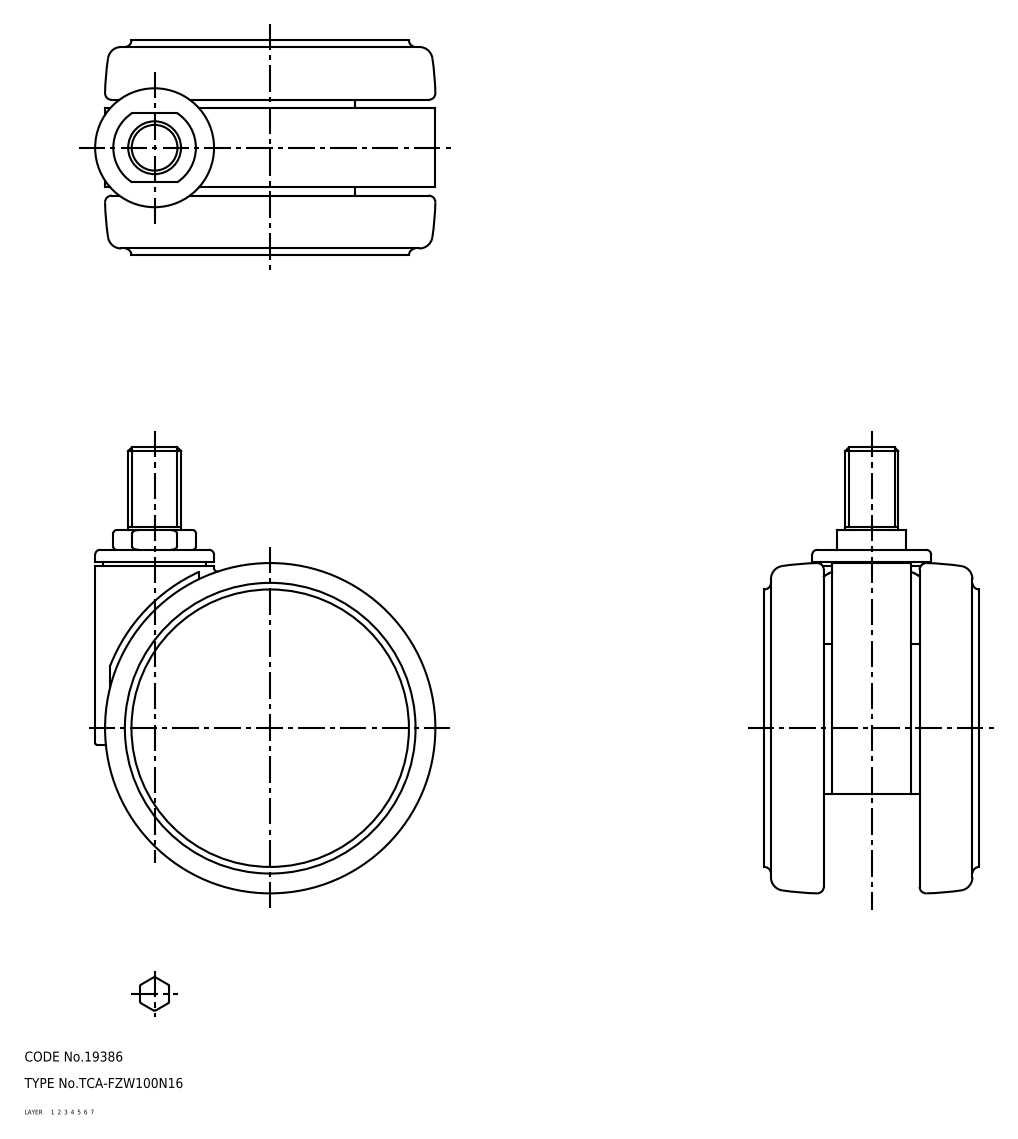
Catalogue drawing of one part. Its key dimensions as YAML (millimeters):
part_name: "caster; TCA-FZW100N16"
step_written_by: "SolidWorks 2015 (AUTOMOTIVE_DESIGN)"
units: millimeters
bodies: {solids: 1, faces: 2344, planar: 792, cylindrical: 1084, other: 468}
overall_size: [135, 103, 65.2]
volume: 299278
surface_area: 123312
round_holes:
  - {diameter: 9.1, count: 1}
  - {diameter: 10, count: 1}
  - {diameter: 10.1, count: 1}
  - {diameter: 10.5, count: 1}
  - {diameter: 12, count: 1}
  - {diameter: 15, count: 1}
  - {diameter: 15.2, count: 1}
  - {diameter: 15.8, count: 1}
  - {diameter: 19.2, count: 1}
  - {diameter: 26, count: 1}
  - {diameter: 28.2, count: 1}
  - {diameter: 30, count: 1}
round_bosses_or_shafts:
  - {diameter: 87.8, count: 1}
  - {diameter: 36, count: 1}
  - {diameter: 31, count: 1}
  - {diameter: 27.9, count: 1}
  - {diameter: 27.6, count: 1}
  - {diameter: 20, count: 1}
  - {diameter: 19, count: 1}
  - {diameter: 18, count: 1}
partial_cylinders:
  - {radius: 0.5, count: 200}
  - {radius: 1.2, count: 160}
  - {radius: 1, count: 81}
  - {radius: 0.2, count: 16}
  - {radius: 2, count: 13}
  - {radius: 0.3, count: 12}
  - {radius: 1.5, count: 8}
  - {radius: 0.8, count: 6}
face_to_face_distances: [1.8, 61.6, 63.4, 3.6, 59.8, 14.5, 16.3, 13.25, 18.1, 47.1]
